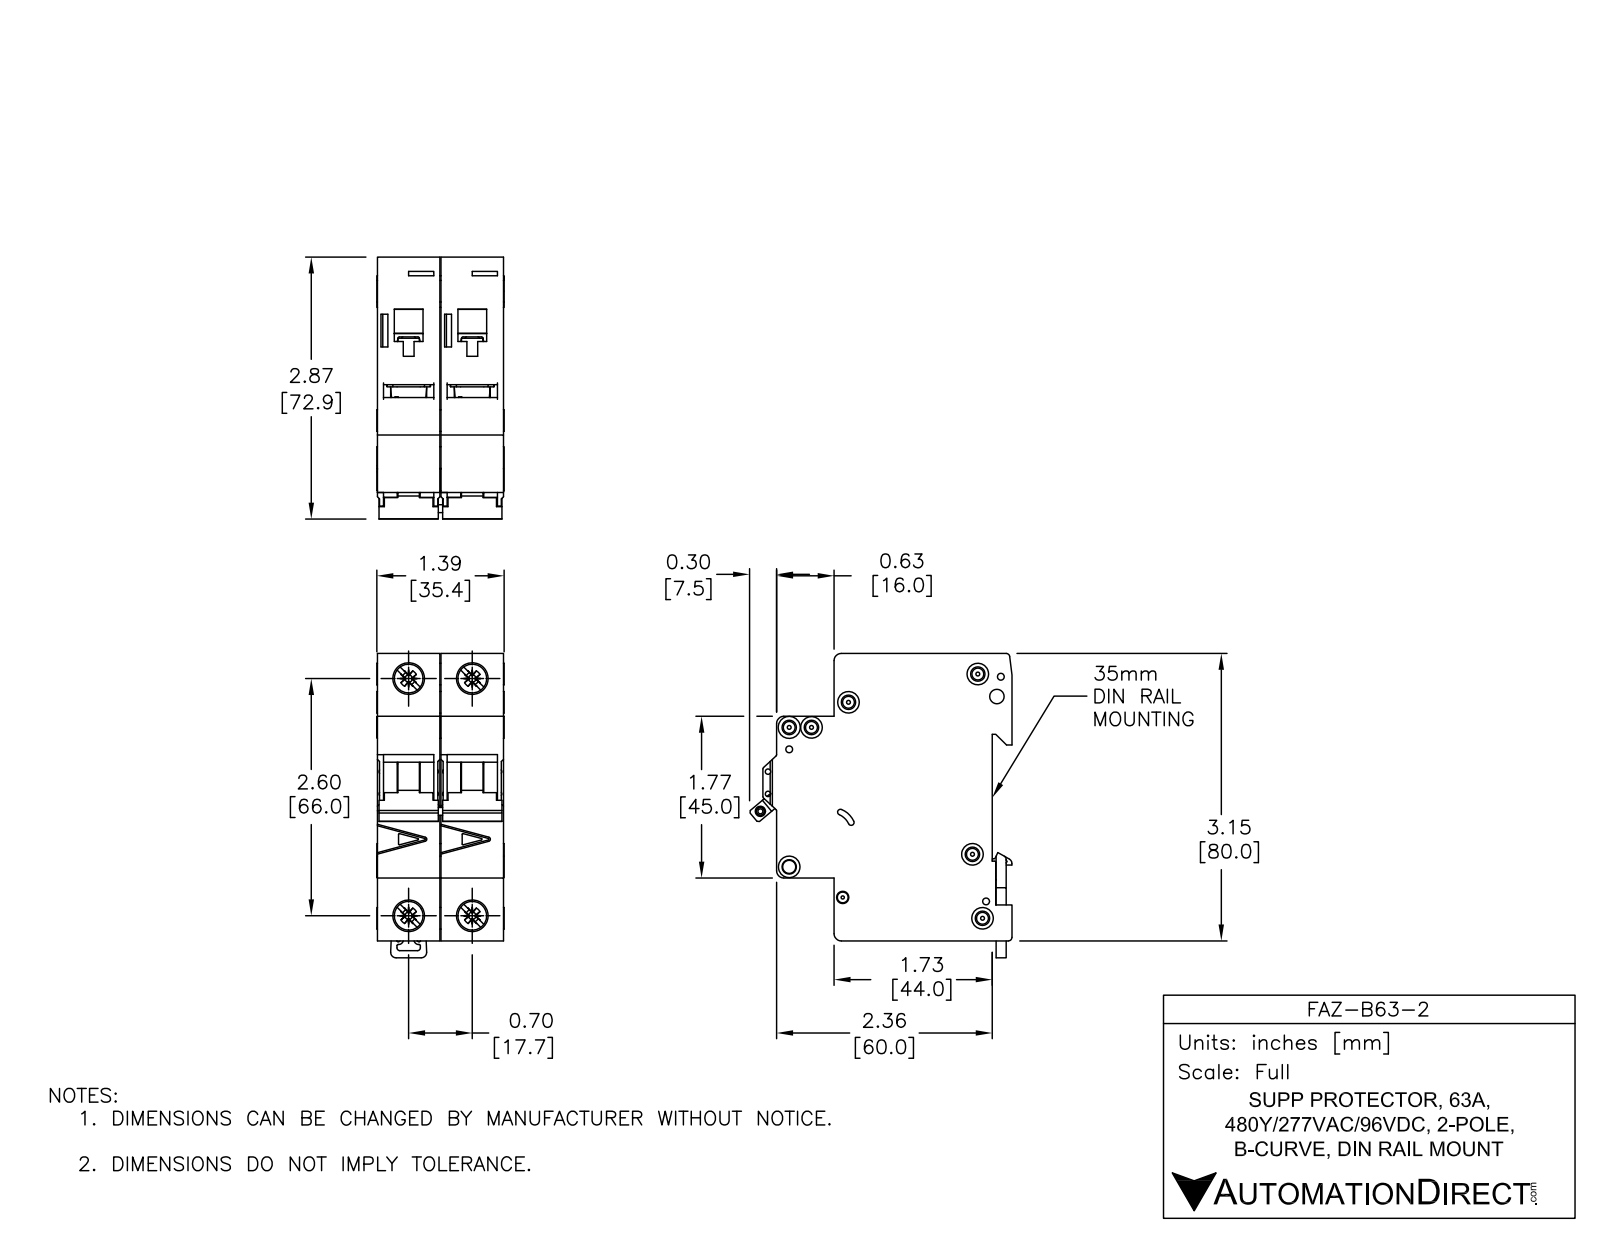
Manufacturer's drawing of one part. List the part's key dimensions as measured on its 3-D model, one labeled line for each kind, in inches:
Part name (STEP PRODUCT): FAZ-B63-2
STEP written by: SolidWorks 2014 (AUTOMOTIVE_DESIGN)
Units: inches
Bodies: 8 solids, 1104 faces (466 planar, 396 cylindrical, 242 other)
Overall size (bounding box): 3.338 × 2.876 × 1.394
Volume: 9.142 in³ · Surface area: 60.14 in²
Round holes (diameter × count): ⌀0.142 ×6, ⌀0.075 ×3, ⌀0.043 ×2, ⌀0.059 ×2, ⌀0.157 ×2, ⌀0.281 ×2, ⌀0.323 ×2, ⌀0.085 ×1, ⌀0.087 ×1, ⌀0.1 ×1, ⌀0.13 ×1, ⌀0.134 ×1
Round bosses / shafts (diameter × count): ⌀0.236 ×4, ⌀0.323 ×2, ⌀0.098 ×2
Partial cylindrical surfaces — rounded edges, fillets, slot ends (radius × count): R0.01 ×49, R0.02 ×19, R0.079 ×10, R0.008 ×8, R0.039 ×8, R0.031 ×2, R0.071 ×2, R0.118 ×2
Main face-to-face distances: 0.697, 0.689, 1.386, 3.129, 0.217, 1.949, 1.732, 2.579, 2.362, 0.63
Hole centre spacings: 0.244, 0.537, 0.697, 2.598, 2.69, 0.189, 0.204, 0.221
